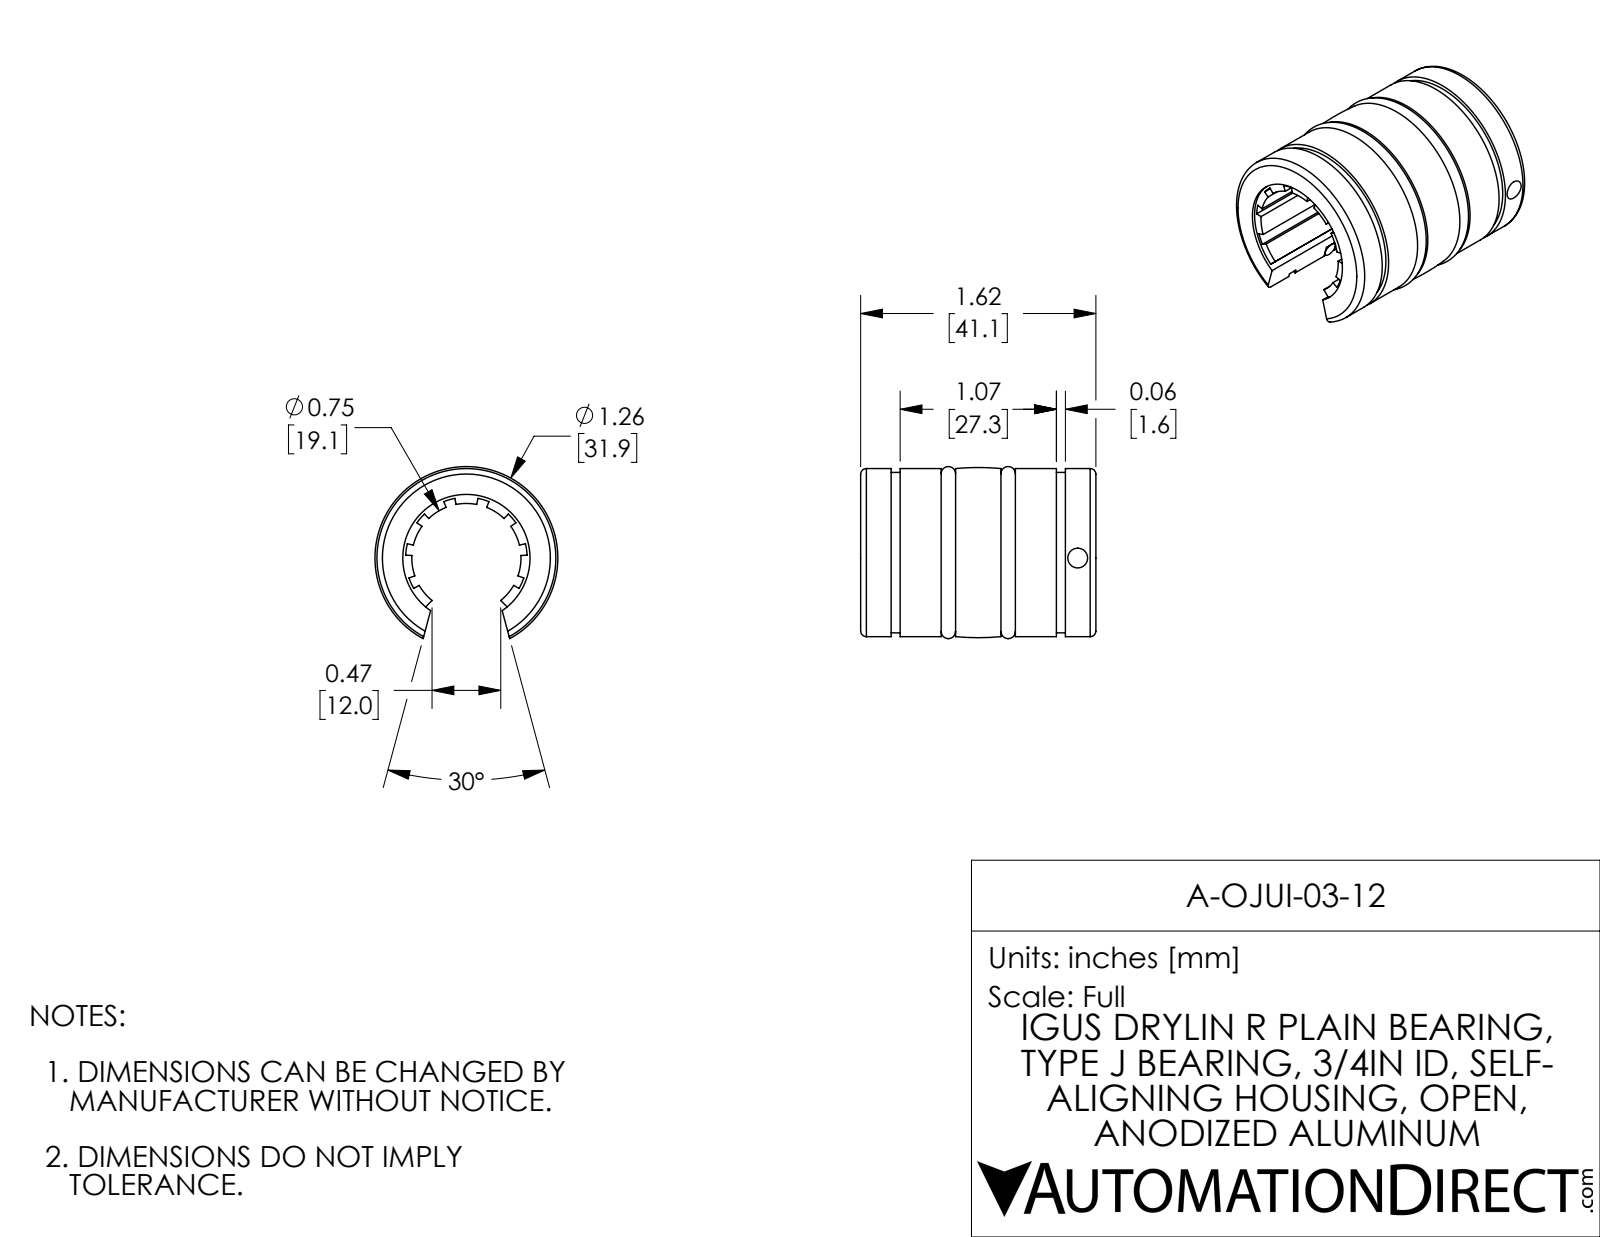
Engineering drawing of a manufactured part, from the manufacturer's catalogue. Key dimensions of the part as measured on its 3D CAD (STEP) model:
Part name (STEP PRODUCT): A-OJUI-03-12
STEP written by: SolidWorks 2017 (AUTOMOTIVE_DESIGN)
Units: inches
Bodies: 4 solids, 136 faces (73 planar, 42 cylindrical, 21 other)
Overall size (bounding box): 1.617 × 1.257 × 1.183
Volume: 0.92 in³ · Surface area: 21.81 in²
Round holes (diameter × count): ⌀0.136 ×1, ⌀0.875 ×1, ⌀0.953 ×1
Round bosses / shafts (diameter × count): ⌀1.23 ×1, ⌀1.177 ×1, ⌀1.059 ×1, ⌀0.134 ×1
Partial cylindrical surfaces — rounded edges, fillets, slot ends (radius × count): R0.375 ×1, R0.418 ×1, R0.469 ×1
Main face-to-face distances: 0.554, 1.064, 0.653, 0.965, 0.099, 0.411, 1.617, 0.715, 0.902, 0.161
